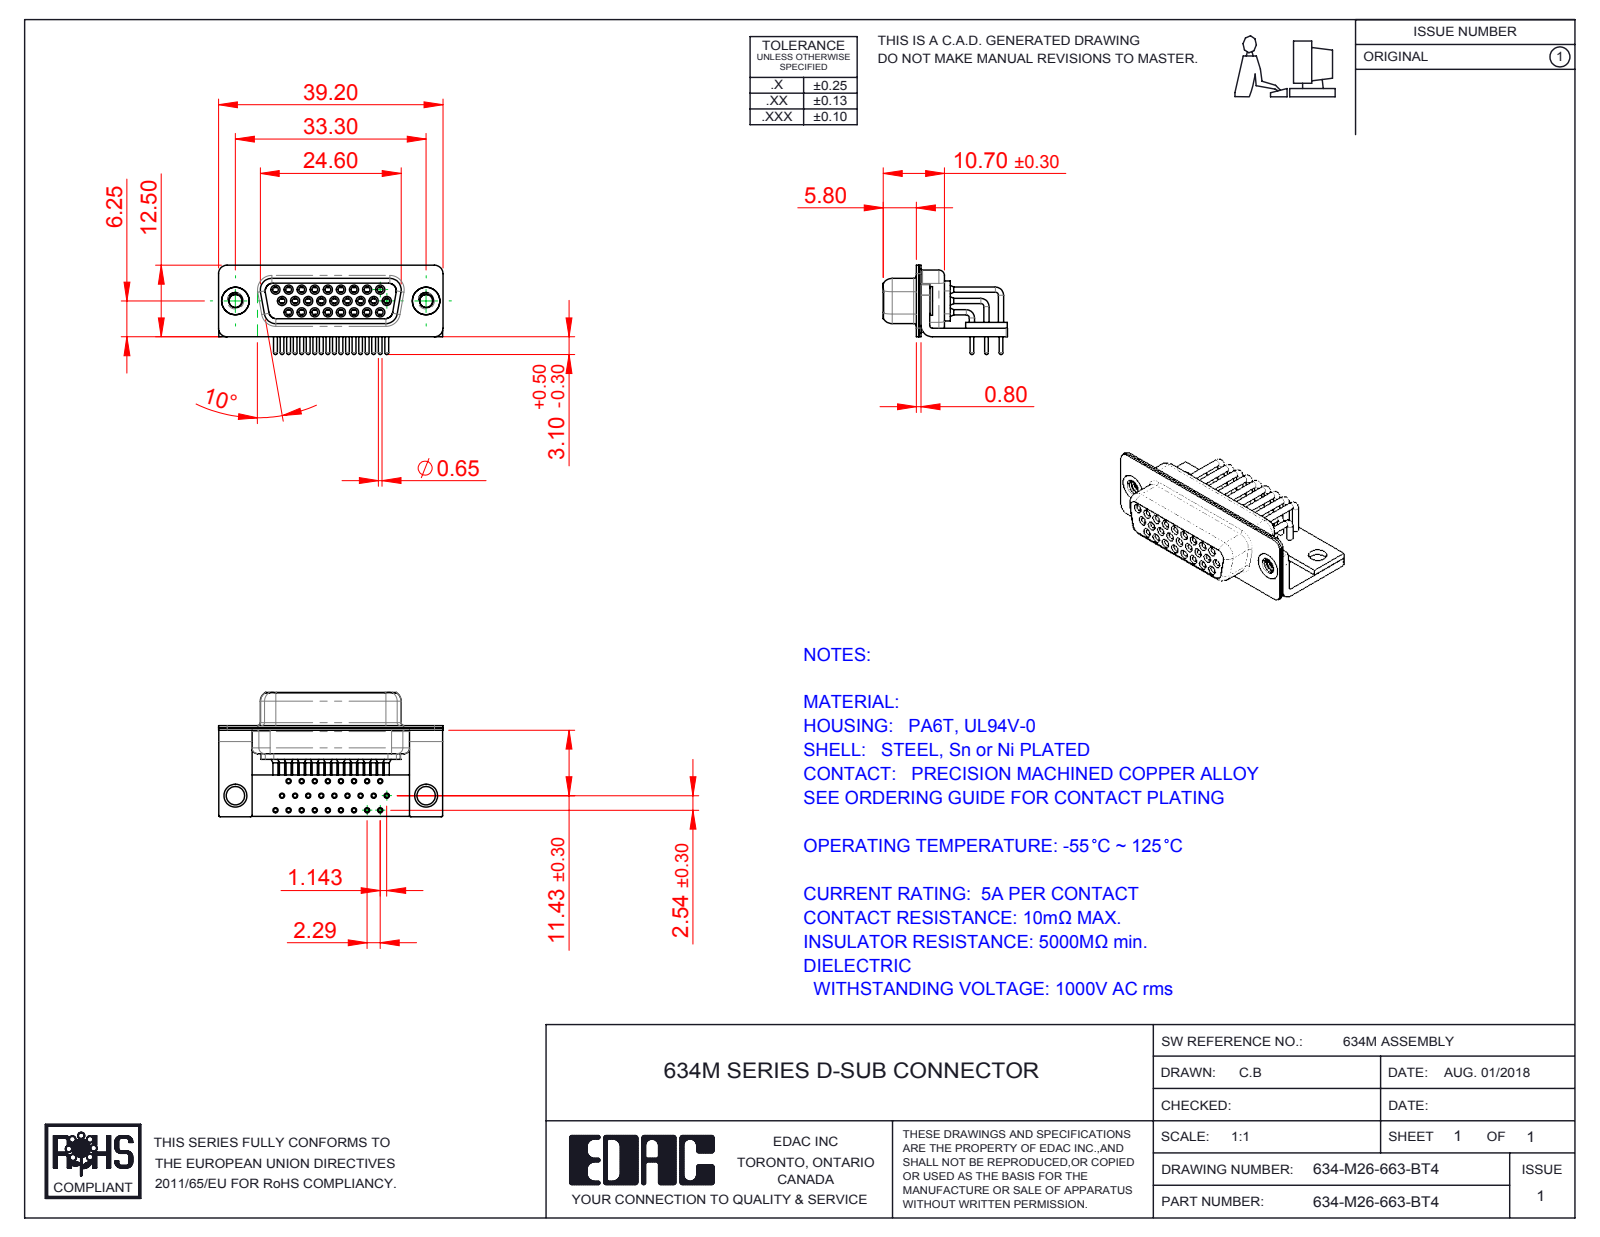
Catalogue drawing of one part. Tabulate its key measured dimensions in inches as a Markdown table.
| quantity | value |
| --- | --- |
| part name | 634M Shell Rear_26 Contacts; 634M Housing_26 Contacts; 634M Contact Row 2; 634-M26-663-BT4 (+6 more) |
| STEP written by | SolidWorks 2016 (CONFIG_CONTROL_DESIGN) |
| units | inches |
| bodies | 34 solids, 1759 faces (483 planar, 809 cylindrical, 467 other) |
| overall size | 1.543 × 0.854 × 0.614 |
| volume | 0.187 in³ |
| surface area | 15.14 in² |
| round holes (diameter × count) | 0.035 × 26, 0.039 × 26, 0.043 × 26, 0.067 × 26, 0.071 × 26, 0.079 × 26, 0.089 × 2, 0.126 × 2, 0.157 × 2, 0.189 × 2 |
| round bosses / shafts (diameter × count) | 0.035 × 27, 0.063 × 26, 0.059 × 26, 0.026 × 26, 0.197 × 2, 0.193 × 2, 0.079 × 1 |
| partial cylindrical surfaces (radius × count) | 0.01 × 16, 0.059 × 16, 0.079 × 13, 0.053 × 8, 0.063 × 8, 0.02 × 5, 0.024 × 4, 0.026 × 4 |
| main face-to-face distances | 0.016, 0.091, 0.031, 0.039, 0.059, 0.075, 0.368, 0.057, 0.352, 0.033 |
| hole center spacings | 0.18, 0.09, 0.09, 0.156, 0.238, 0.27, 0.168, 0.109 |
